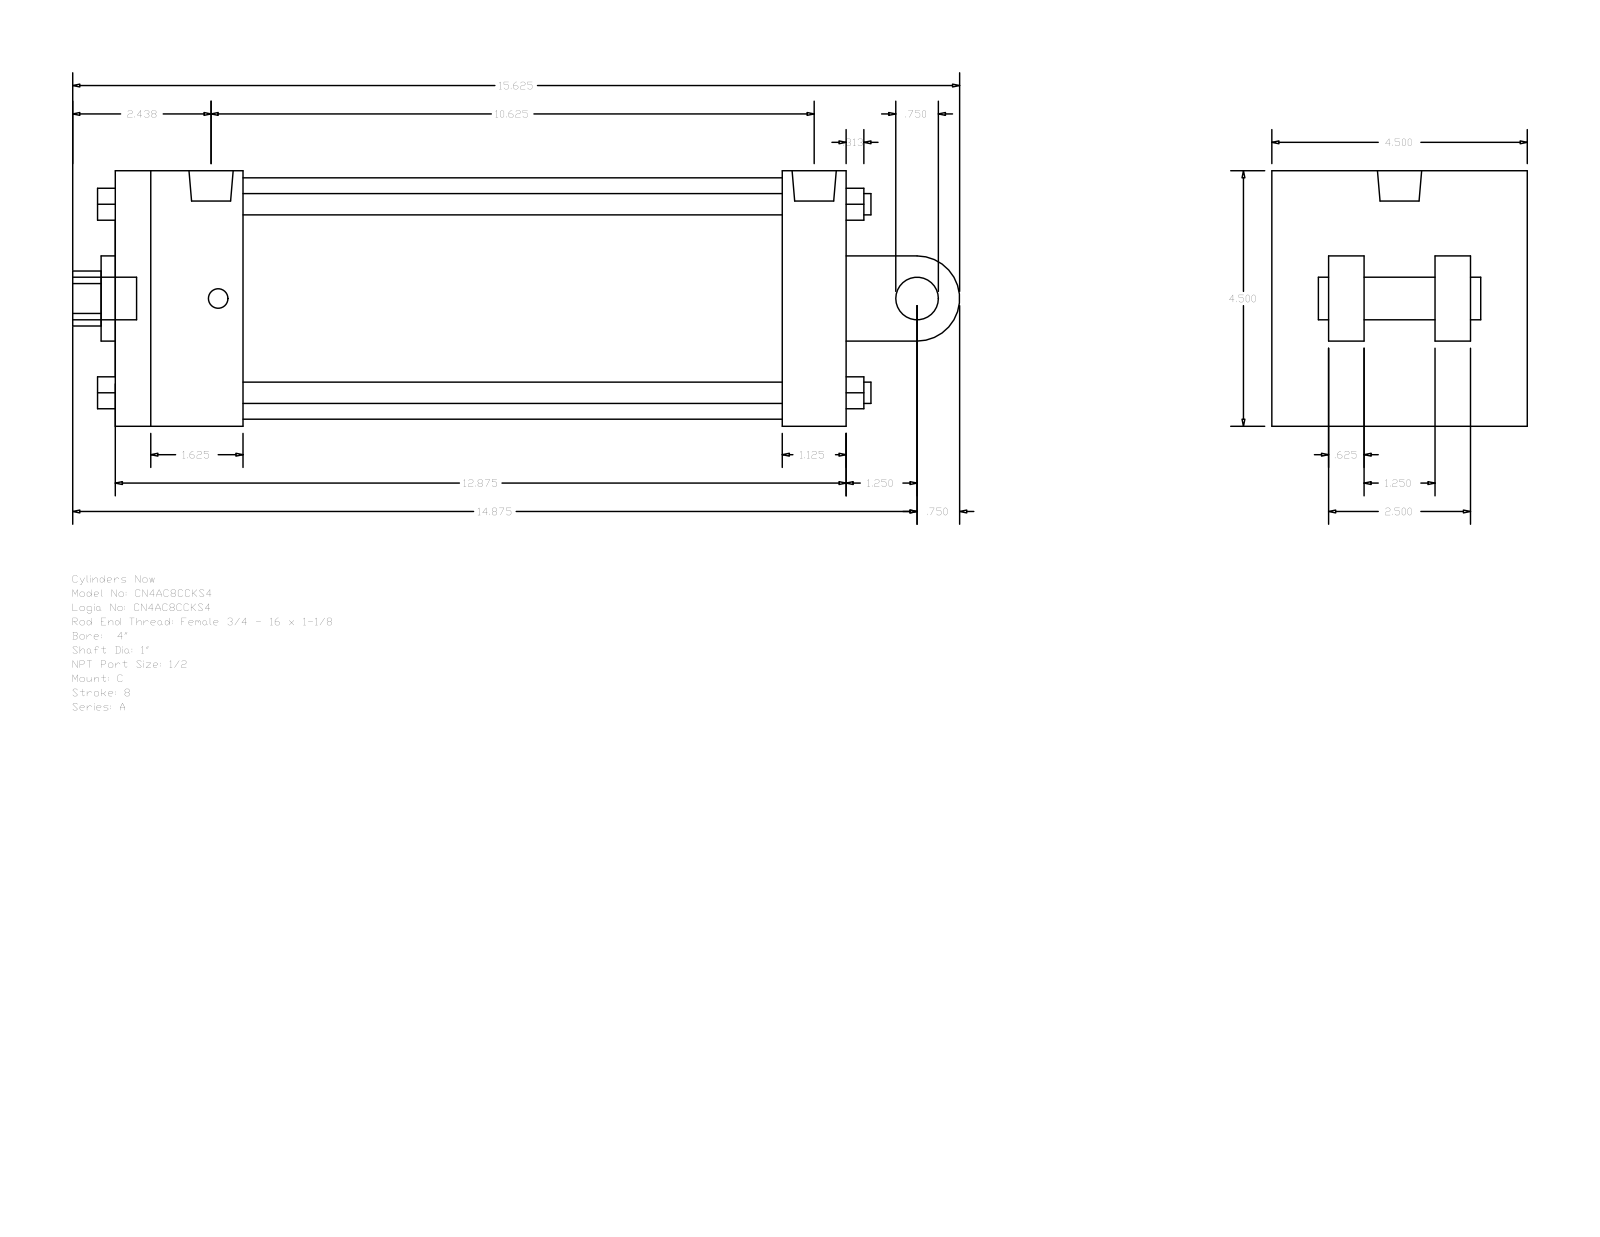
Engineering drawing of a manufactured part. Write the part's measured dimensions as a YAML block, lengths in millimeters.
part_name: "A_C__0400_1"
step_written_by: "GSSL Pune (CONFIG_CONTROL_DESIGN)"
units: millimeters
bodies: {solids: 0, faces: 135, planar: 102, cylindrical: 33, other: 0}
overall_size: [396.88, 114.3, 114.3]
round_holes:
  - {diameter: 8.73, count: 2}
  - {diameter: 19.77, count: 1}
  - {diameter: 25.4, count: 1}
  - {diameter: 38.1, count: 1}
  - {diameter: 107.95, count: 1}
round_bosses_or_shafts:
  - {diameter: 9.53, count: 4}
  - {diameter: 19.05, count: 2}
  - {diameter: 8.73, count: 2}
  - {diameter: 19.77, count: 1}
partial_cylinders:
  - {radius: 12.29, count: 1}
  - {radius: 19.05, count: 1}
face_to_face_distances: [114.3, 327.02, 73.03, 28.57, 298.45, 57.15, 241.3, 269.87, 15.87, 47.63]
hole_center_spacings: [3.18]
